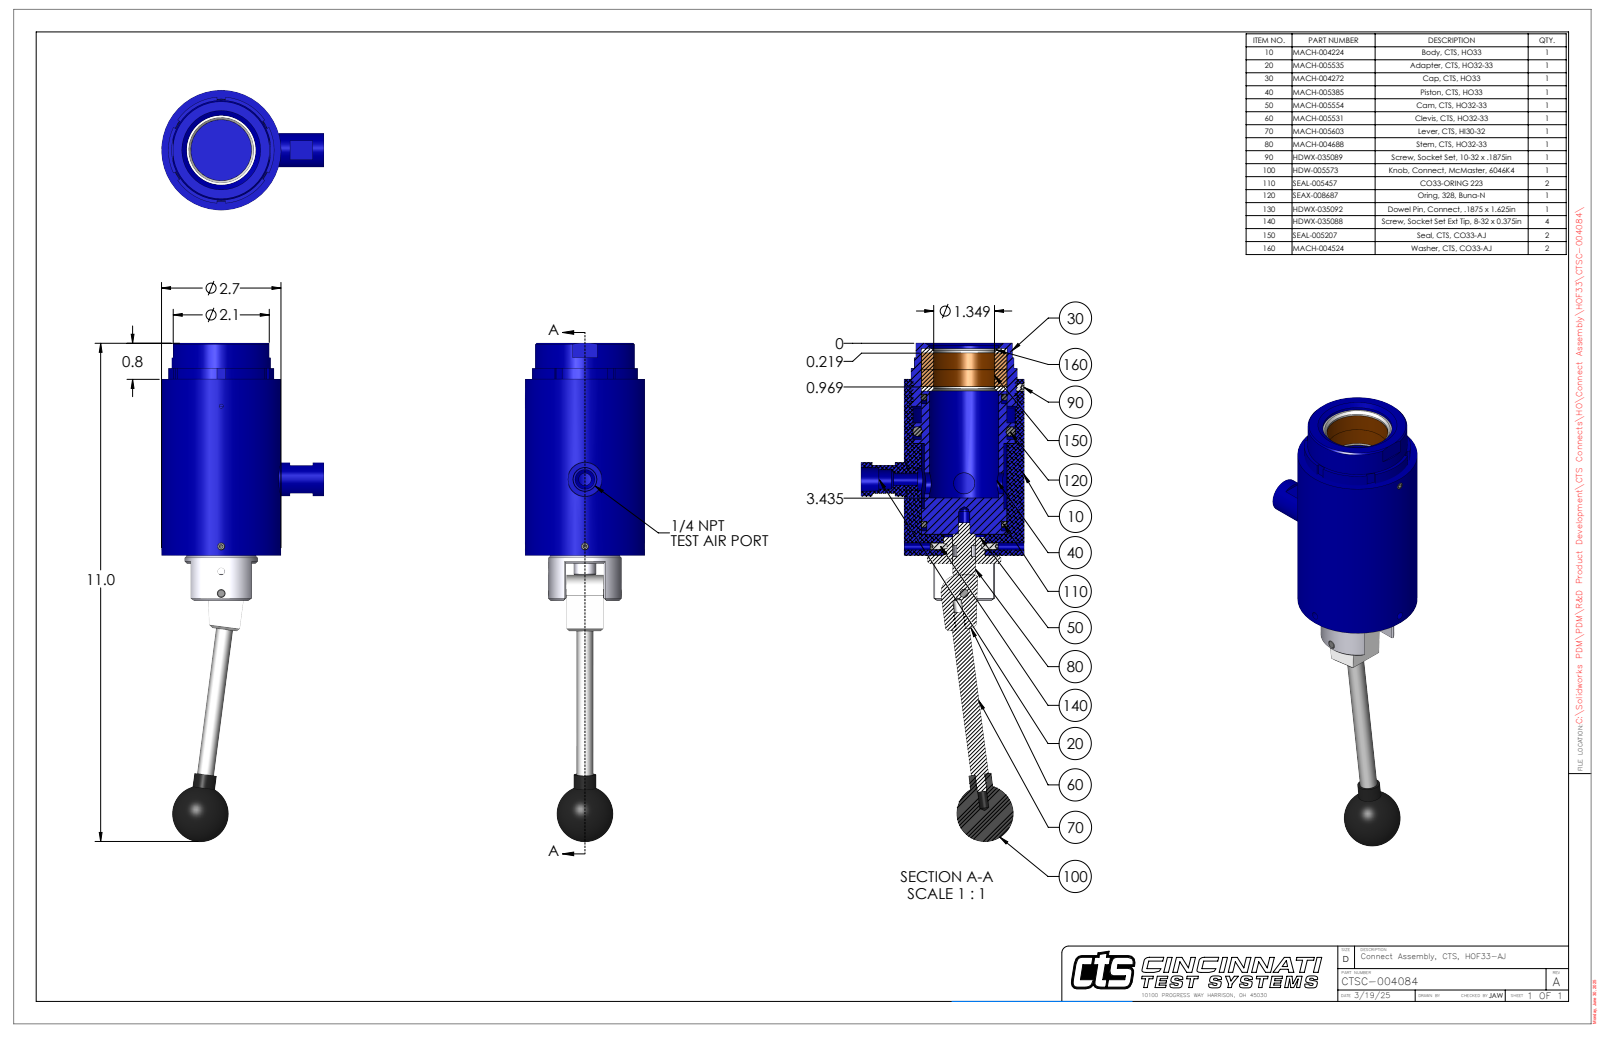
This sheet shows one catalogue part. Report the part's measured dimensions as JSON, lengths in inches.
{"part_name": "CTSC-004084", "step_written_by": "SolidWorks 2023 (AUTOMOTIVE_DESIGN)", "units": "inches", "bodies": {"solids": 14, "faces": 546, "planar": 179, "cylindrical": 226, "other": 141}, "overall_size": [11.05, 3.6, 2.65], "volume_in3": 21.65, "surface_area_in2": 132.2, "round_holes": [[0.201, 3], [0.159, 2], [0.469, 2], [0.094, 1], [0.189, 1], [0.19, 1], [0.25, 1], [0.281, 1], [0.438, 1], [0.5, 1], [0.516, 1], [0.527, 1]], "round_bosses_or_shafts": [[0.75, 2], [0.5, 2], [0.164, 2], [0.109, 2], [2.65, 1], [2.344, 1], [2.2, 1], [1.885, 1]], "partial_cylinders_radius": [[0.385, 1], [0.4, 1], [1.13, 1], [1.181, 1]], "face_to_face_distances": [0.844, 0.094, 0.75, 4.489, 3.739, 0.375, 0.375, 4.114, 0.469, 4.583], "hole_center_spacings": [0.089, 0.488, 1.71, 1.948, 2.033, 2.122, 2.436, 3.658]}
